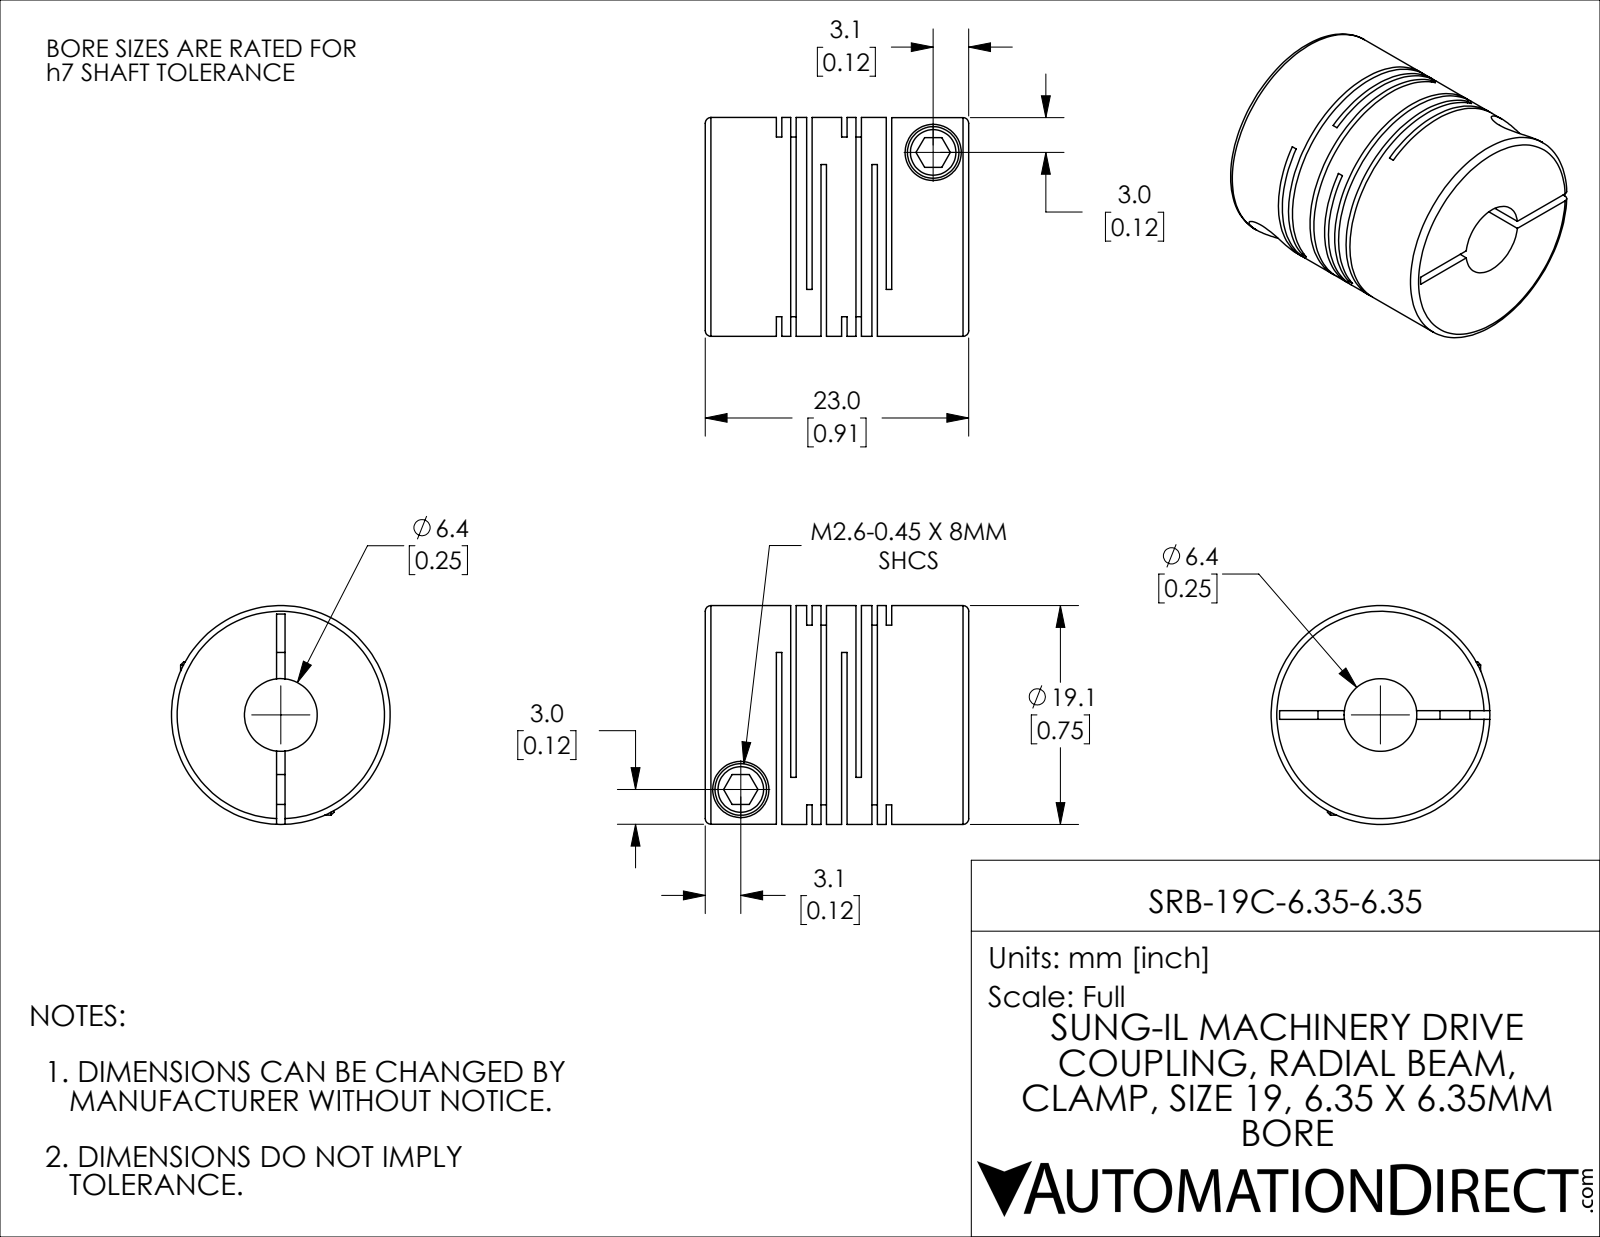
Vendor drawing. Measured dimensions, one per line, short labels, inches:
name: SRB-19C-6.35-6.35
written by: SolidWorks 2021 (CONFIG_CONTROL_DESIGN)
unit: in
bodies: 1 solid, 114 faces (60 planar, 42 cylindrical, 12 other)
size: 0.906 × 0.752 × 0.752
volume: 0.294 in³; area: 9.249 in²
holes: 2× ⌀0.102, 2× ⌀0.193, 1× ⌀0.25
bosses: 2× ⌀0.177, 1× ⌀0.752
face distances: 0.019, 0.049, 0.104, 0.224, 0.085, 0.12, 0.175, 0.206, 0.03, 0.055
